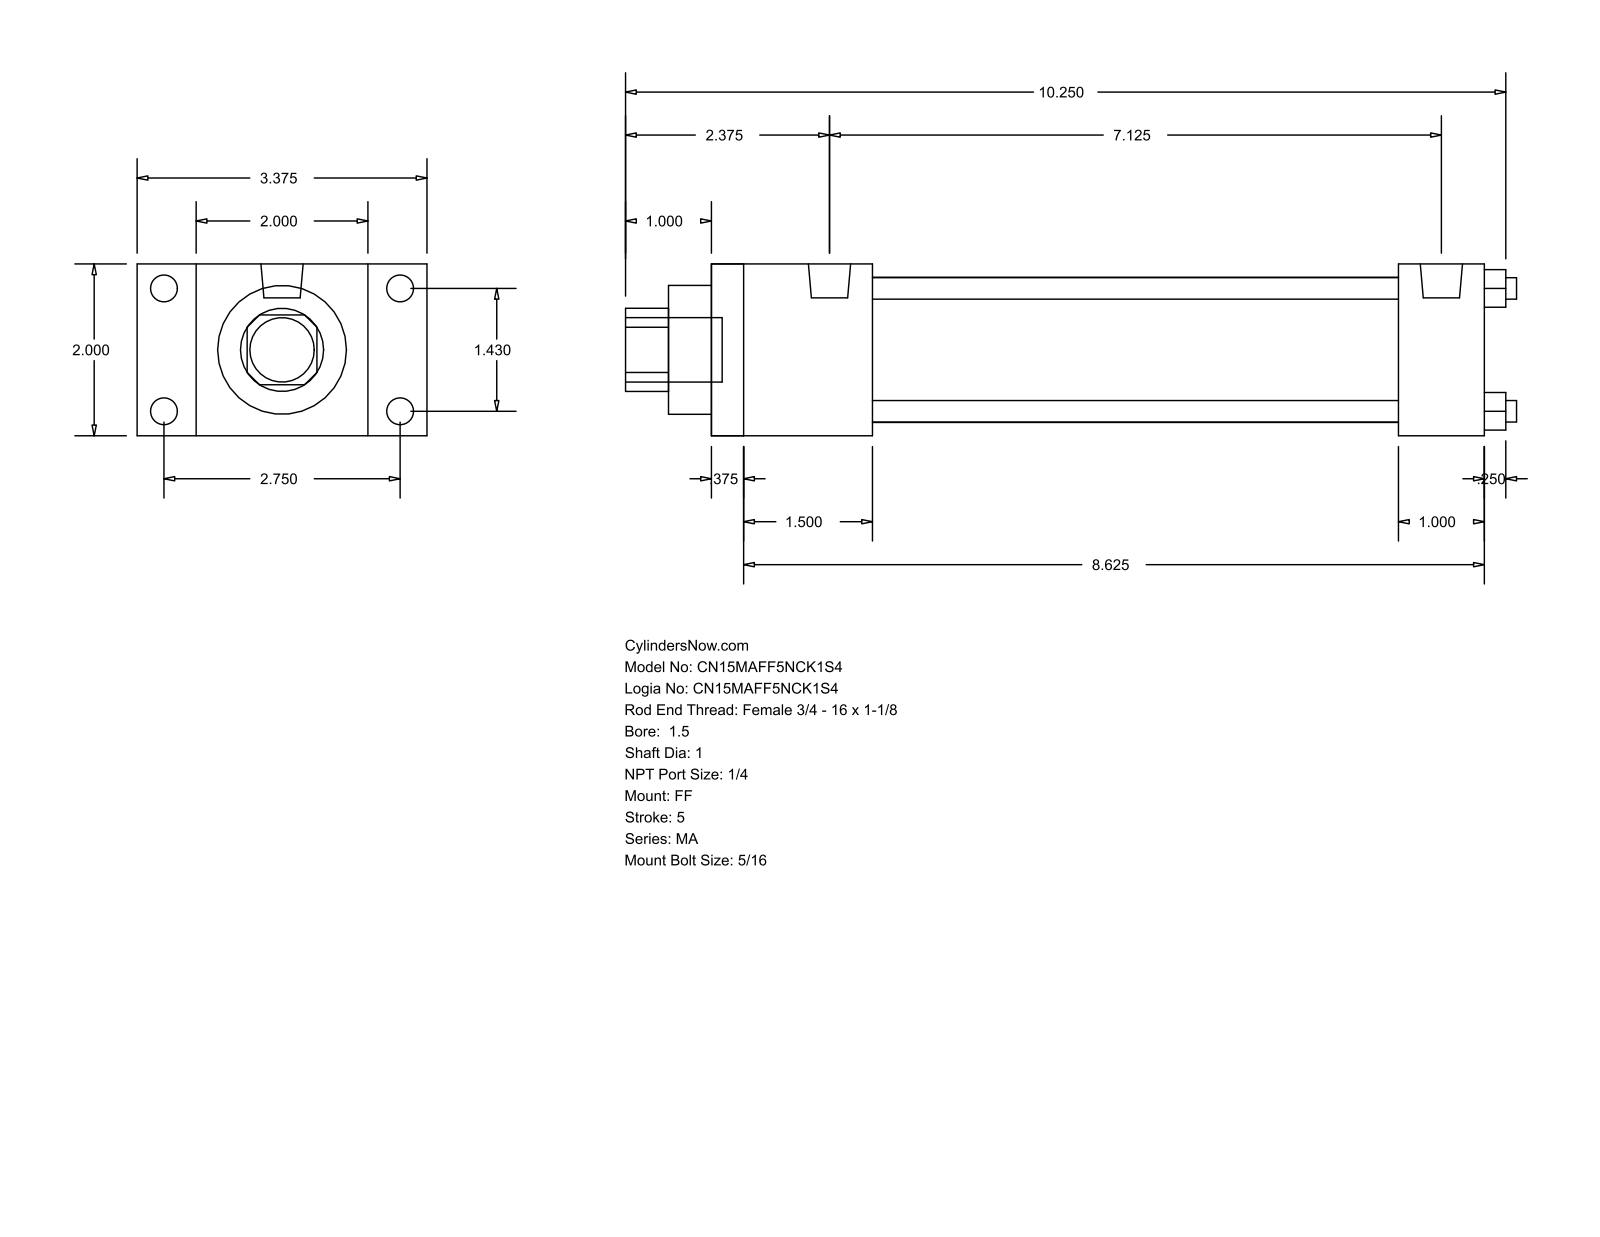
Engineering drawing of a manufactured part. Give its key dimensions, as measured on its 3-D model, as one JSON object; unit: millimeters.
{"part_name": "MA_FF__0150_1", "step_written_by": "GSSL Pune (CONFIG_CONTROL_DESIGN)", "units": "millimeters", "bodies": {"solids": 0, "faces": 92, "planar": 64, "cylindrical": 28, "other": 0}, "overall_size": [263.52, 85.72, 50.8], "round_holes": [[6.35, 4], [25.4, 1], [38.1, 1], [42.93, 1]], "round_bosses_or_shafts": [[7.94, 8], [12.49, 2], [19.05, 1]], "partial_cylinders_radius": [[12.29, 1]], "face_to_face_distances": [50.8, 228.6, 9.52, 219.08, 25.4, 47.63, 203.2, 38.11, 193.68, 155.57], "hole_center_spacings": [25.68, 36.32, 51.36]}
